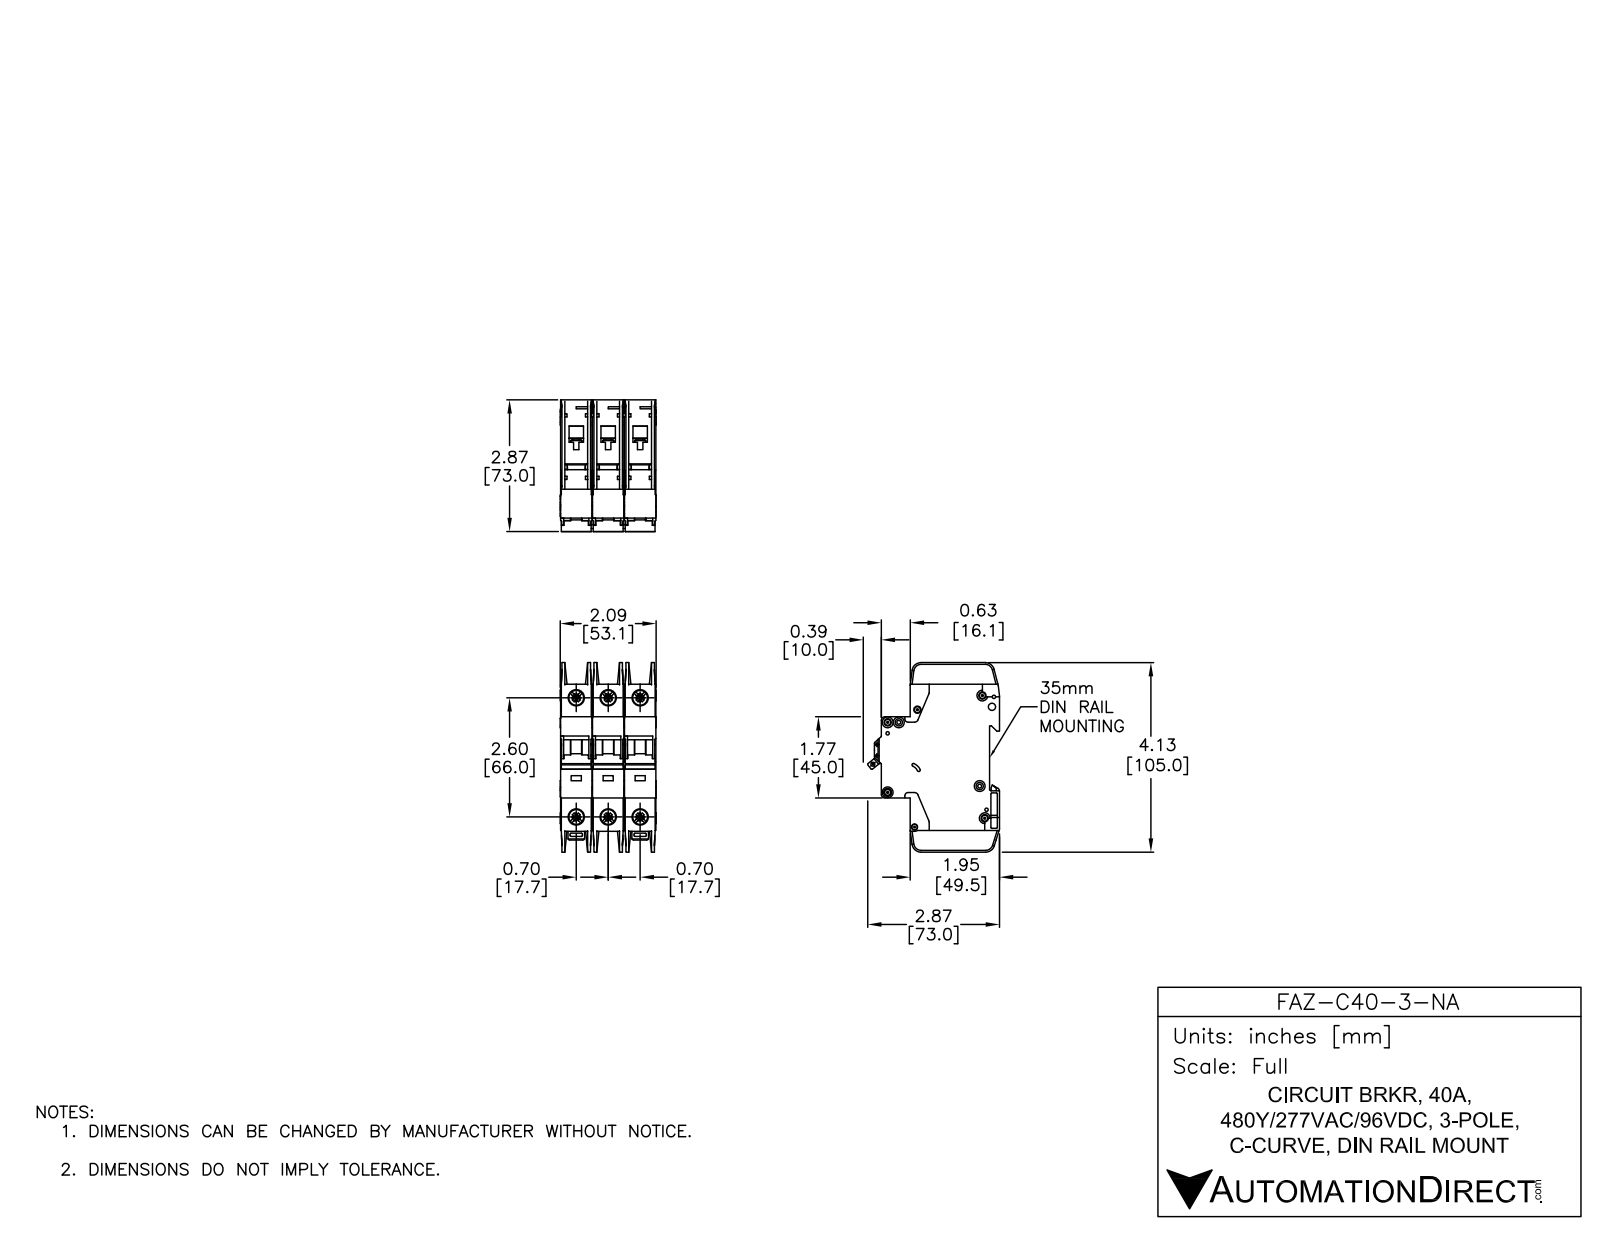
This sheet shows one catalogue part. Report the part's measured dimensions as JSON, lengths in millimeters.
{"part_name": "FAZ-C40-3-NA", "step_written_by": "SolidWorks 2014 (AUTOMOTIVE_DESIGN)", "units": "millimeters", "bodies": {"solids": 9, "faces": 2352, "planar": 1227, "cylindrical": 789, "other": 336}, "overall_size": [105, 73.04, 53.1], "volume_mm3": 233085, "surface_area_mm2": 74219, "round_holes": [[3.6, 7], [7.15, 6], [8.2, 6], [1.09, 2], [1.5, 2], [4, 2], [1.9, 1], [2.15, 1], [2.2, 1], [2.55, 1], [3.3, 1], [3.4, 1]], "round_bosses_or_shafts": [[6, 7], [2.5, 3]], "partial_cylinders_radius": [[0.25, 65], [0.5, 30], [1, 26], [2, 14], [1.8, 5], [5, 5], [4, 4], [0.2, 2]], "face_to_face_distances": [17.7, 35.4, 17.5, 35.2, 0.7, 15.05, 2.45, 1.75, 15.75, 13.3], "hole_center_spacings": [17.7, 68.33, 66, 6.2, 35.4, 74.89, 5.19, 6.1]}
